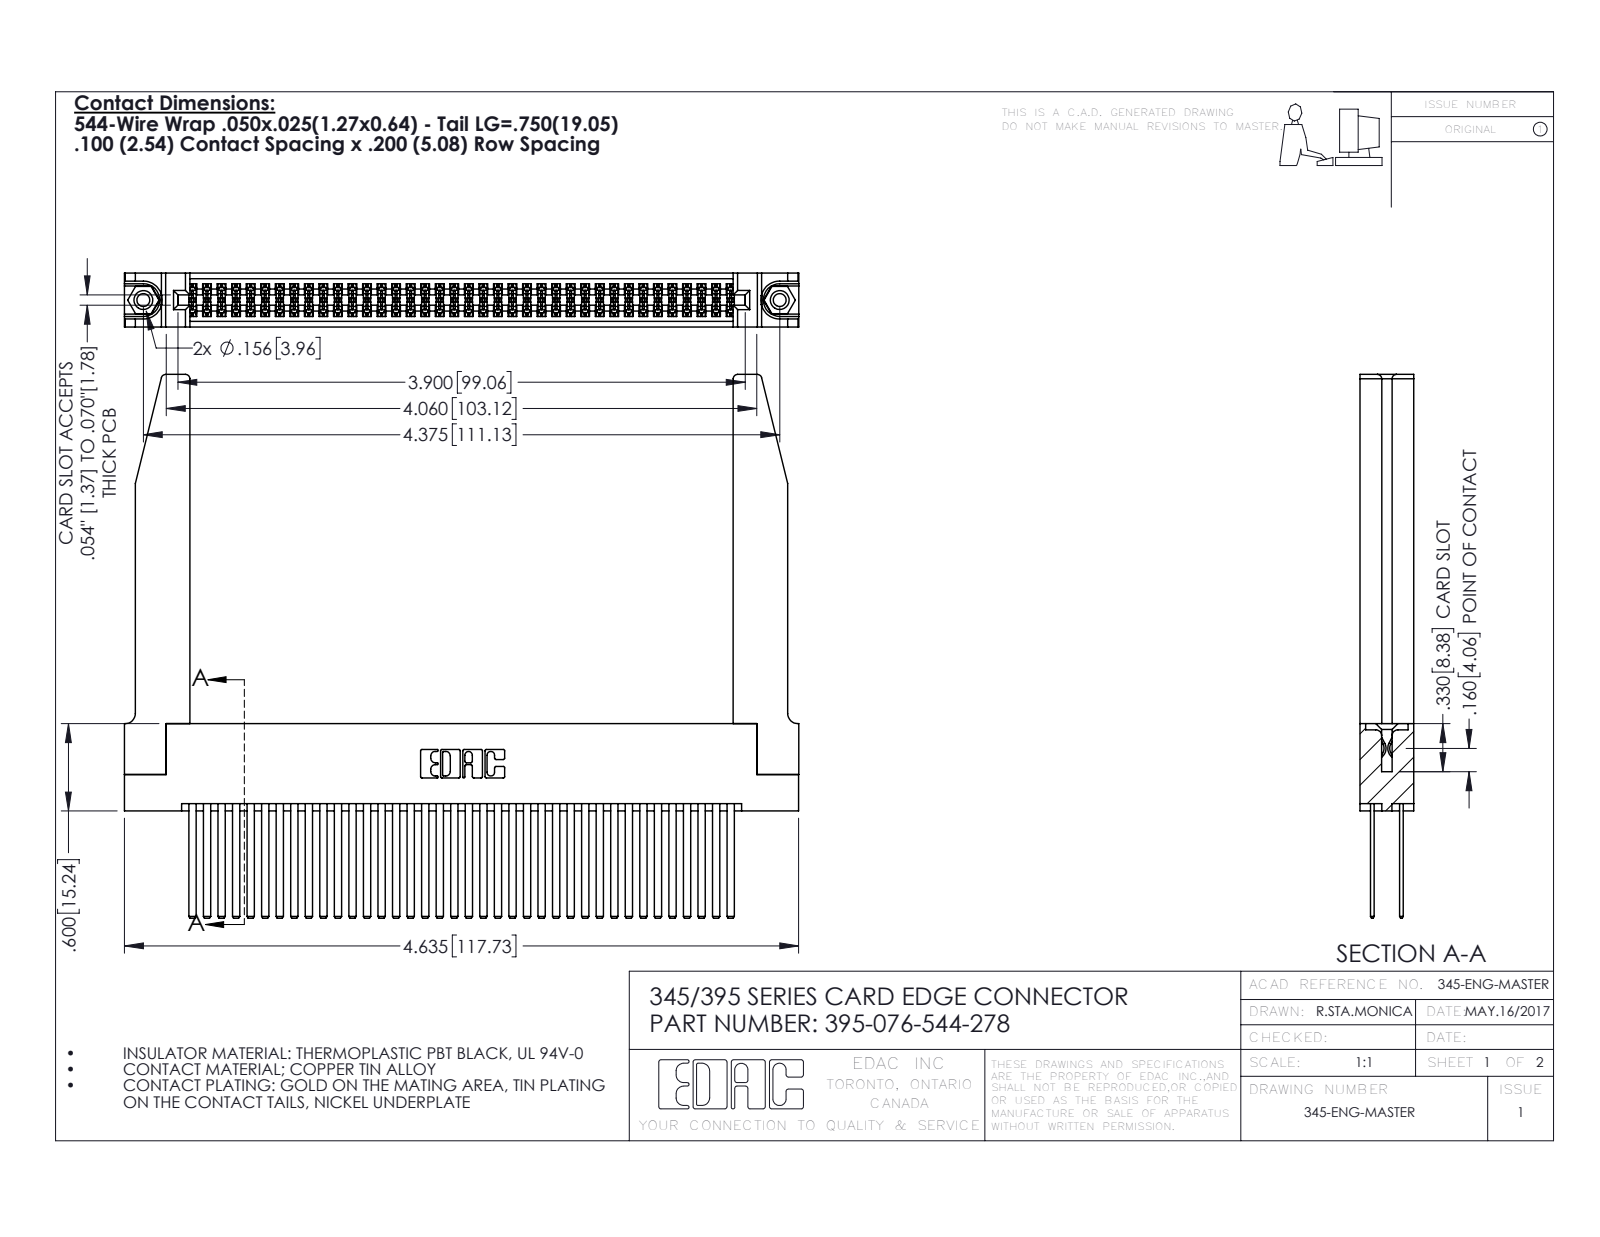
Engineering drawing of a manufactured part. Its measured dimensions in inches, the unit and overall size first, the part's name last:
Units: inches
Overall size (bounding box): 4.636 × 3.737 × 0.37
Round holes (diameter × count): ⌀0.089 ×2, ⌀0.125 ×2, ⌀0.156 ×2, ⌀0.064 ×1
Round bosses / shafts (diameter × count): ⌀0.155 ×2
Partial cylindrical surfaces — rounded edges, fillets, slot ends (radius × count): R0.006 ×114, R0.01 ×22, R0.03 ×8, R0.007 ×6, R0.031 ×6, R0.026 ×3, R0.014 ×2, R0.019 ×2
Main face-to-face distances: 0.072, 0.298, 0.2, 0.098, 0.272, 0.025, 0.37, 0.225, 0.175, 0.148
Hole centre spacings: 0.27, 4.139, 4.375
Volume: 1.235 in³ · Surface area: 43.88 in²
Bodies: 81 solids, 3704 faces (2426 planar, 1226 cylindrical, 52 other)
Part name (STEP PRODUCT): 345-250-001_345-250-001-102; 345-220-078_345-220-078; 345-292-001_345-293-144; 345 Part_Flush Mounting Lugs - 0.156 Dia-TH (+1 more)
STEP written by: SolidWorks 2016 (CONFIG_CONTROL_DESIGN)
